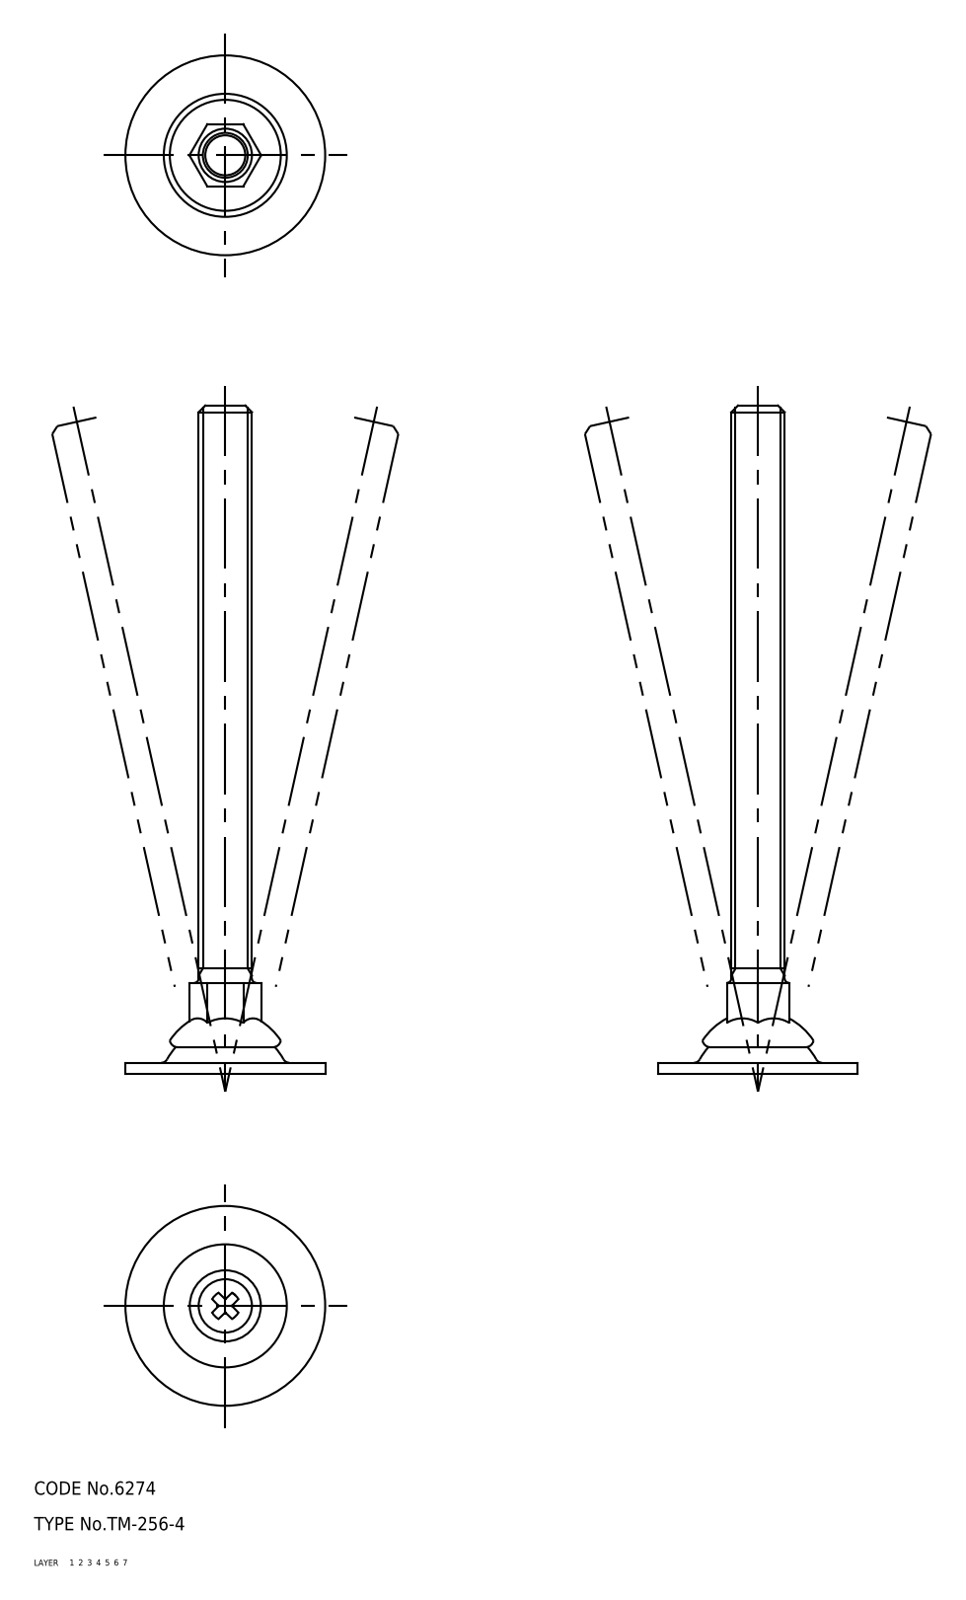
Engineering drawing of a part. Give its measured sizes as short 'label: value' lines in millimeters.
name: 67112897; 67112910; 67112923; 67112936
written by: CADfix (AUTOMOTIVE_DESIGN)
unit: mm
bodies: 4 solids, 74 faces (0 planar, 0 cylindrical, 74 other)
size: 150.5 × 45 × 45
volume: 21 984 mm³; area: 11 567 mm²
